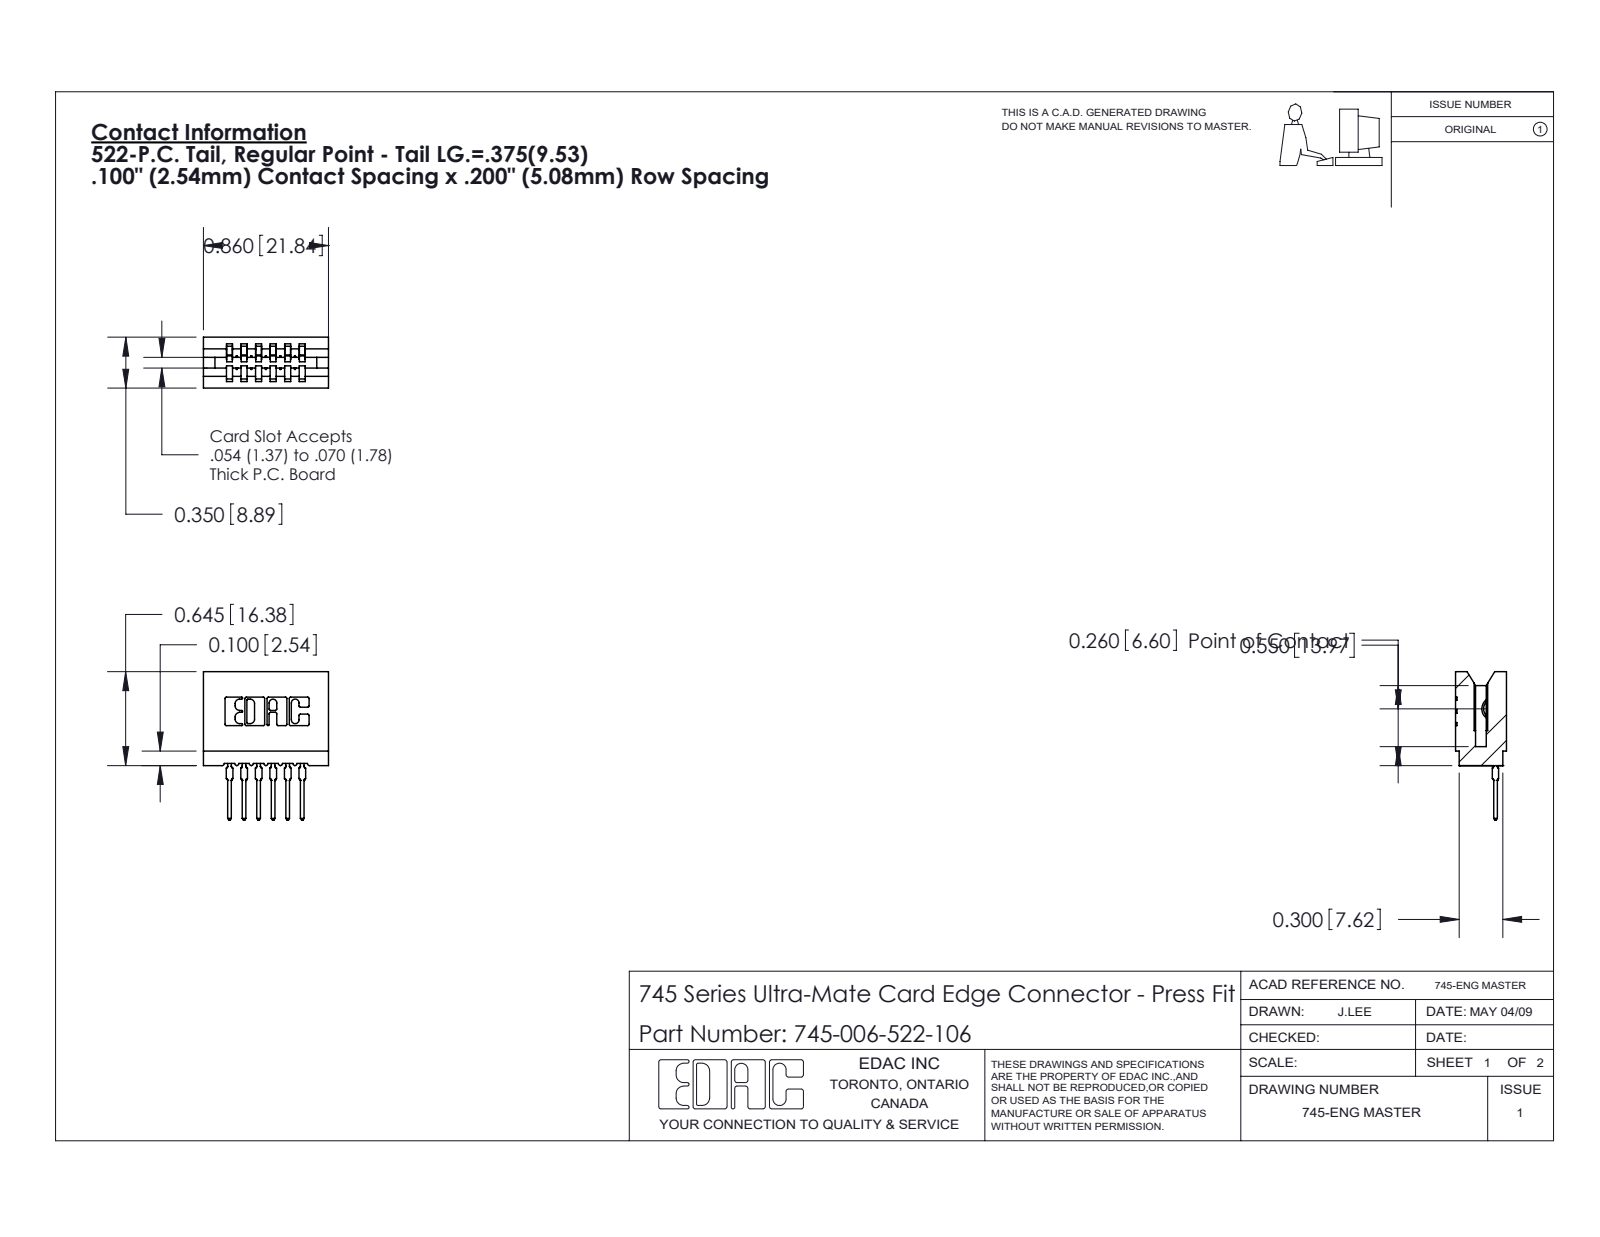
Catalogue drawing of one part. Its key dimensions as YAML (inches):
part_name: "745-292-001_522; 745 Part_Insulator Option - 06; 745-006-522-106"
step_written_by: "SolidWorks 2020 (CONFIG_CONTROL_DESIGN)"
units: inches
bodies: {solids: 7, faces: 768, planar: 458, cylindrical: 154, other: 156}
overall_size: [1.021, 0.86, 0.35]
volume: 0.129
surface_area: 5.053
partial_cylinders:
  - {radius: 0.01, count: 22}
  - {radius: 0.015, count: 12}
  - {radius: 0.021, count: 12}
  - {radius: 0.007, count: 6}
  - {radius: 0.031, count: 6}
  - {radius: 0.005, count: 4}
  - {radius: 0.011, count: 4}
  - {radius: 0.026, count: 3}
face_to_face_distances: [0.1, 0.2, 0.3, 0.042, 0.142, 0.058, 0.242, 0.158, 0.4, 0.35]
